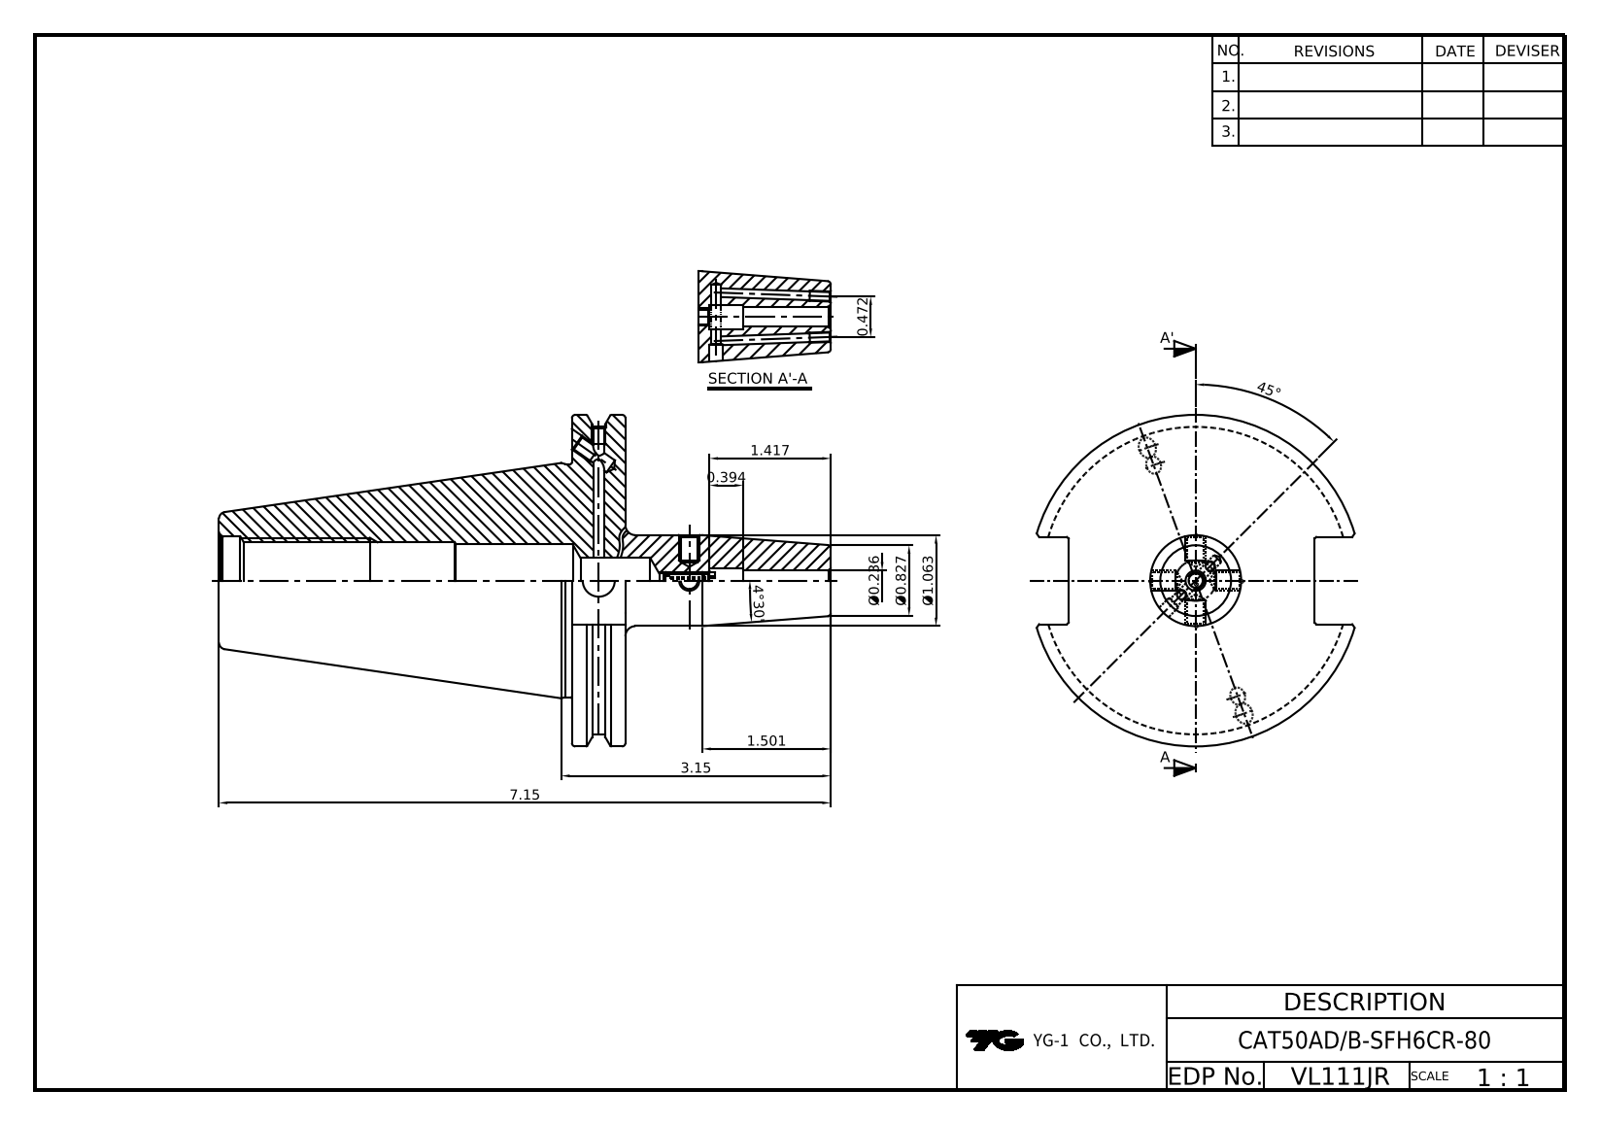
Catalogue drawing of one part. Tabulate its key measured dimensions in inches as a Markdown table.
| quantity | value |
| --- | --- |
| part name | VL111JR |
| STEP written by | Autodesk Inventor 2024 (AUTOMOTIVE_DESIGN) |
| units | inches |
| bodies | 1 solid, 92 faces (37 planar, 30 cylindrical, 25 other) |
| overall size | 7.15 × 3.875 × 3.728 |
| volume | 21.32 in³ |
| surface area | 79.35 in² |
| round holes (diameter × count) | 0.097 × 2, 0.128 × 2, 0.163 × 2, 0.165 × 2, 0.197 × 2, 0.169 × 1, 0.236 × 1, 0.283 × 1, 0.375 × 1, 0.531 × 1, 0.846 × 1, 0.865 × 1 |
| round bosses / shafts (diameter × count) | 3.875 × 1, 3.594 × 1, 2.726 × 1, 1.063 × 1 |
| main face-to-face distances | 0.625, 4.125, 4.75, 2.875, 1.02, 7.15, 3.025, 2.4, 4.513, 0.389 |
